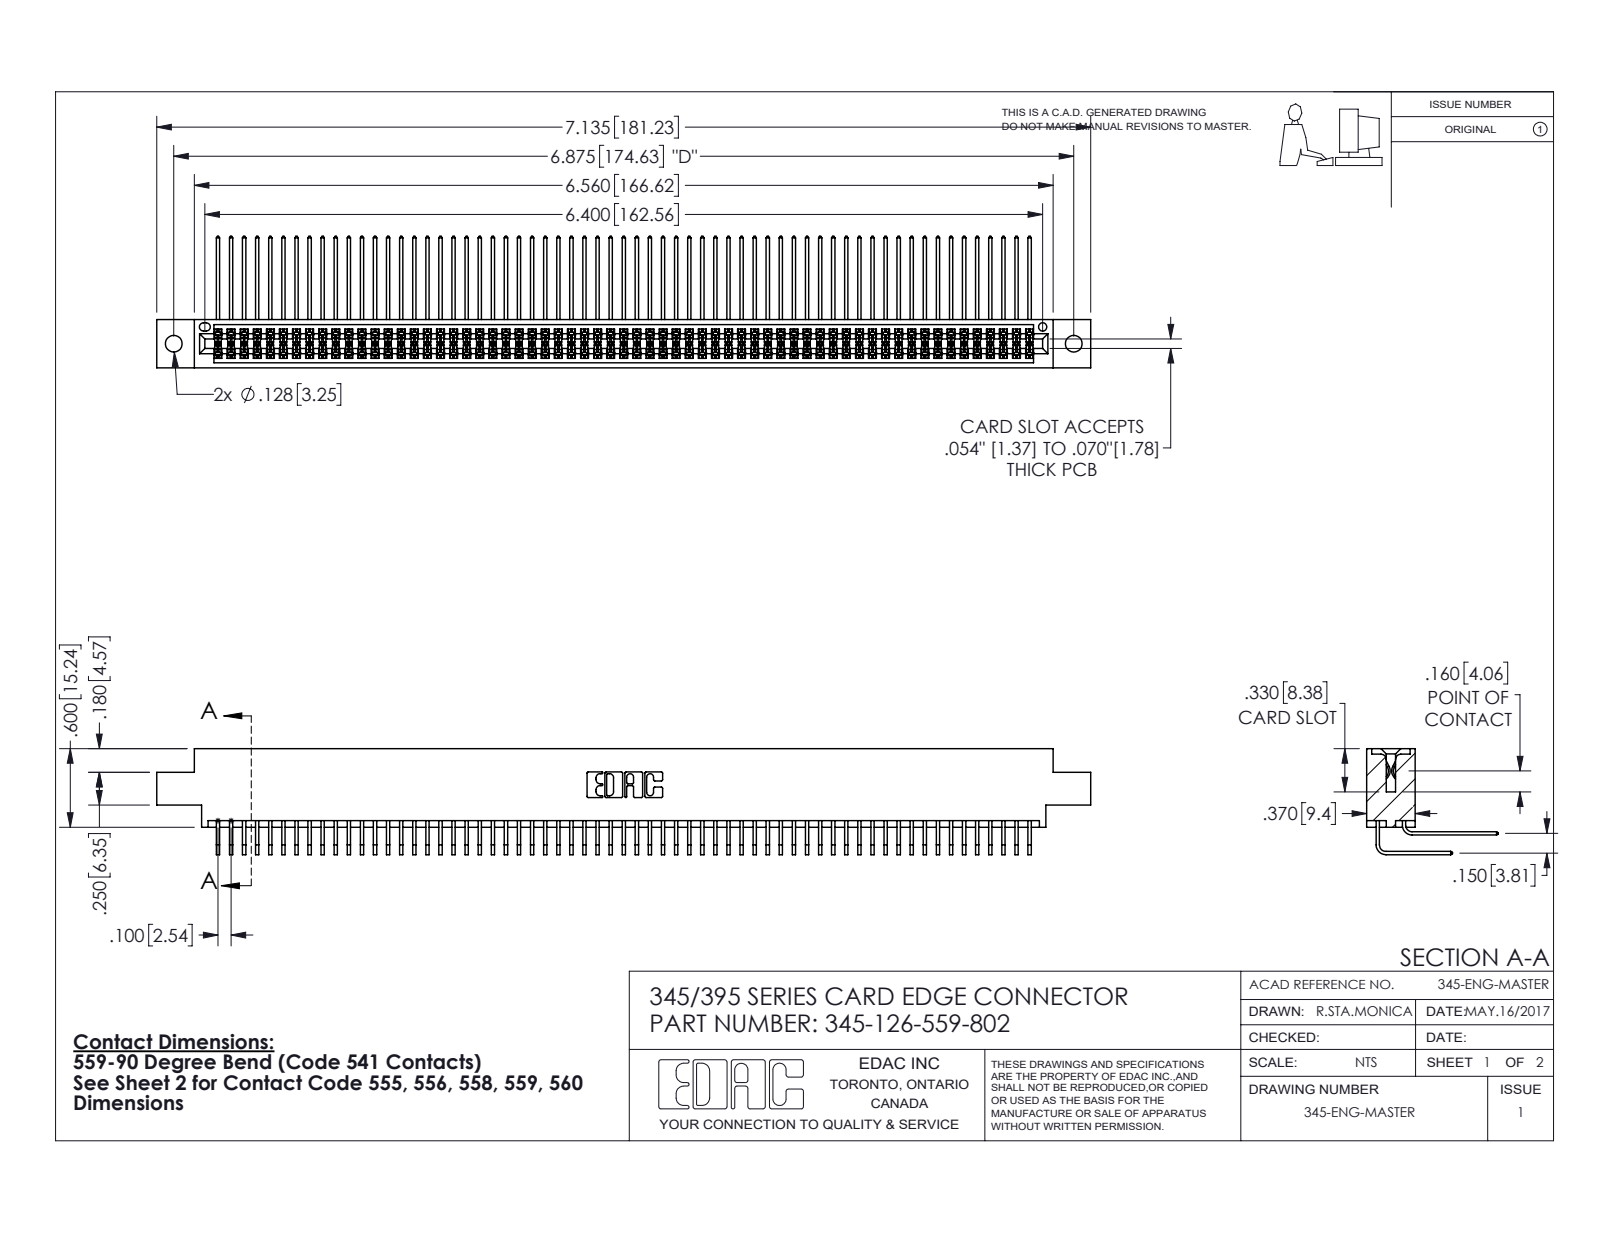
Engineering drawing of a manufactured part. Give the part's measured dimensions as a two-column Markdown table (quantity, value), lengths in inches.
| quantity | value |
| --- | --- |
| part name | 345-126-559-802; 345-292-001_558 559 Tail - 1; 345-292-001_559 Tail - 2; 345 Part_0.170 Offset - 0.128 Dia |
| STEP written by | SolidWorks 2016 (CONFIG_CONTROL_DESIGN) |
| units | inches |
| bodies | 127 solids, 6682 faces (4494 planar, 2188 cylindrical, 0 other) |
| overall size | 7.135 × 1.005 × 0.809 |
| volume | 1.121 in³ |
| surface area | 47.83 in² |
| round holes (diameter × count) | 0.128 × 2, 0.064 × 1 |
| partial cylindrical surfaces (radius × count) | 0.006 × 251, 0.01 × 22, 0.007 × 6, 0.031 × 6, 0.026 × 3, 0.014 × 2, 0.019 × 2, 0.022 × 2 |
| main face-to-face distances | 0.072, 0.298, 0.37, 0.2, 0.098, 0.272, 0.025, 0.225, 0.175, 0.15 |
| hole center spacings | 0.27, 6.639, 6.875 |
